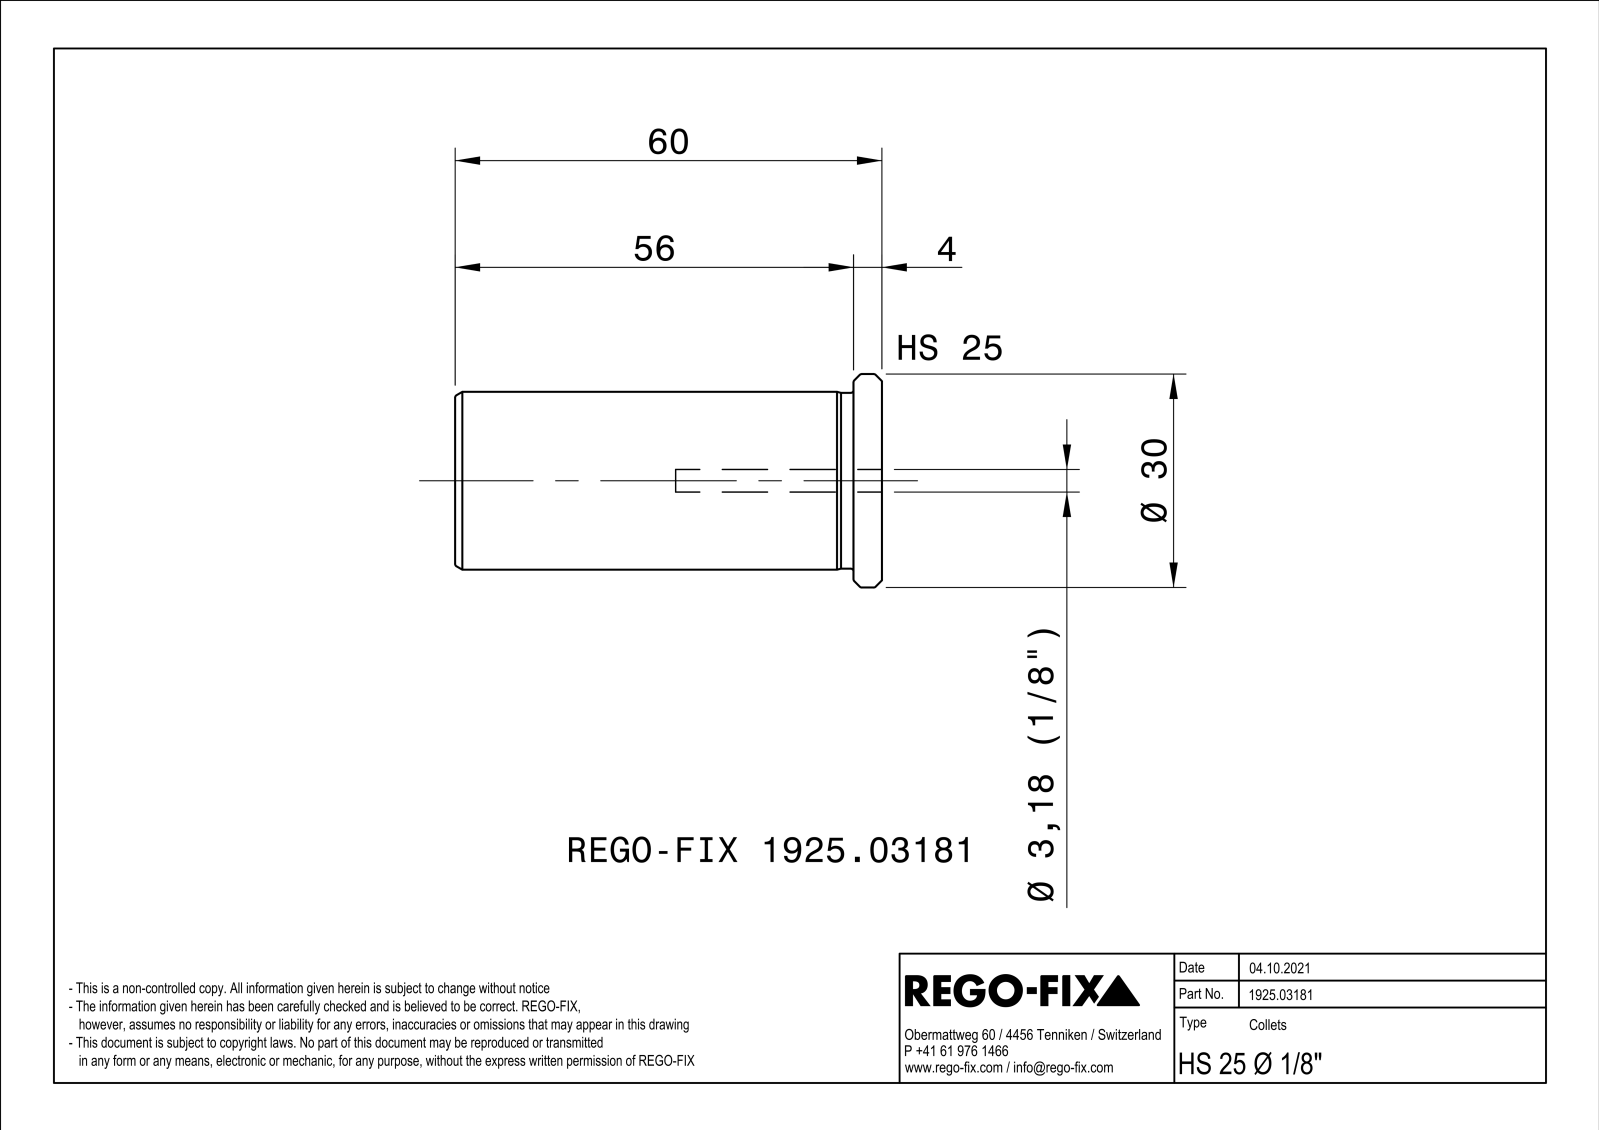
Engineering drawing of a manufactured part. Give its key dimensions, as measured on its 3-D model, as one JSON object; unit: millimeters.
{"part_name": "NOCUT", "step_written_by": "SIEMENS PLM Software Solid Edge ST10 (AUTOMOTIVE_DESIGN)", "units": "millimeters", "bodies": {"solids": 1, "faces": 72, "planar": 22, "cylindrical": 12, "other": 38}, "overall_size": [60, 29.99, 29.99], "volume_mm3": 23623, "surface_area_mm2": 9906, "round_holes": [[3.17, 1], [10, 1], [20.5, 1]], "round_bosses_or_shafts": [[30, 1], [25, 1], [24.7, 1]], "face_to_face_distances": [0.8, 4, 60, 56]}
